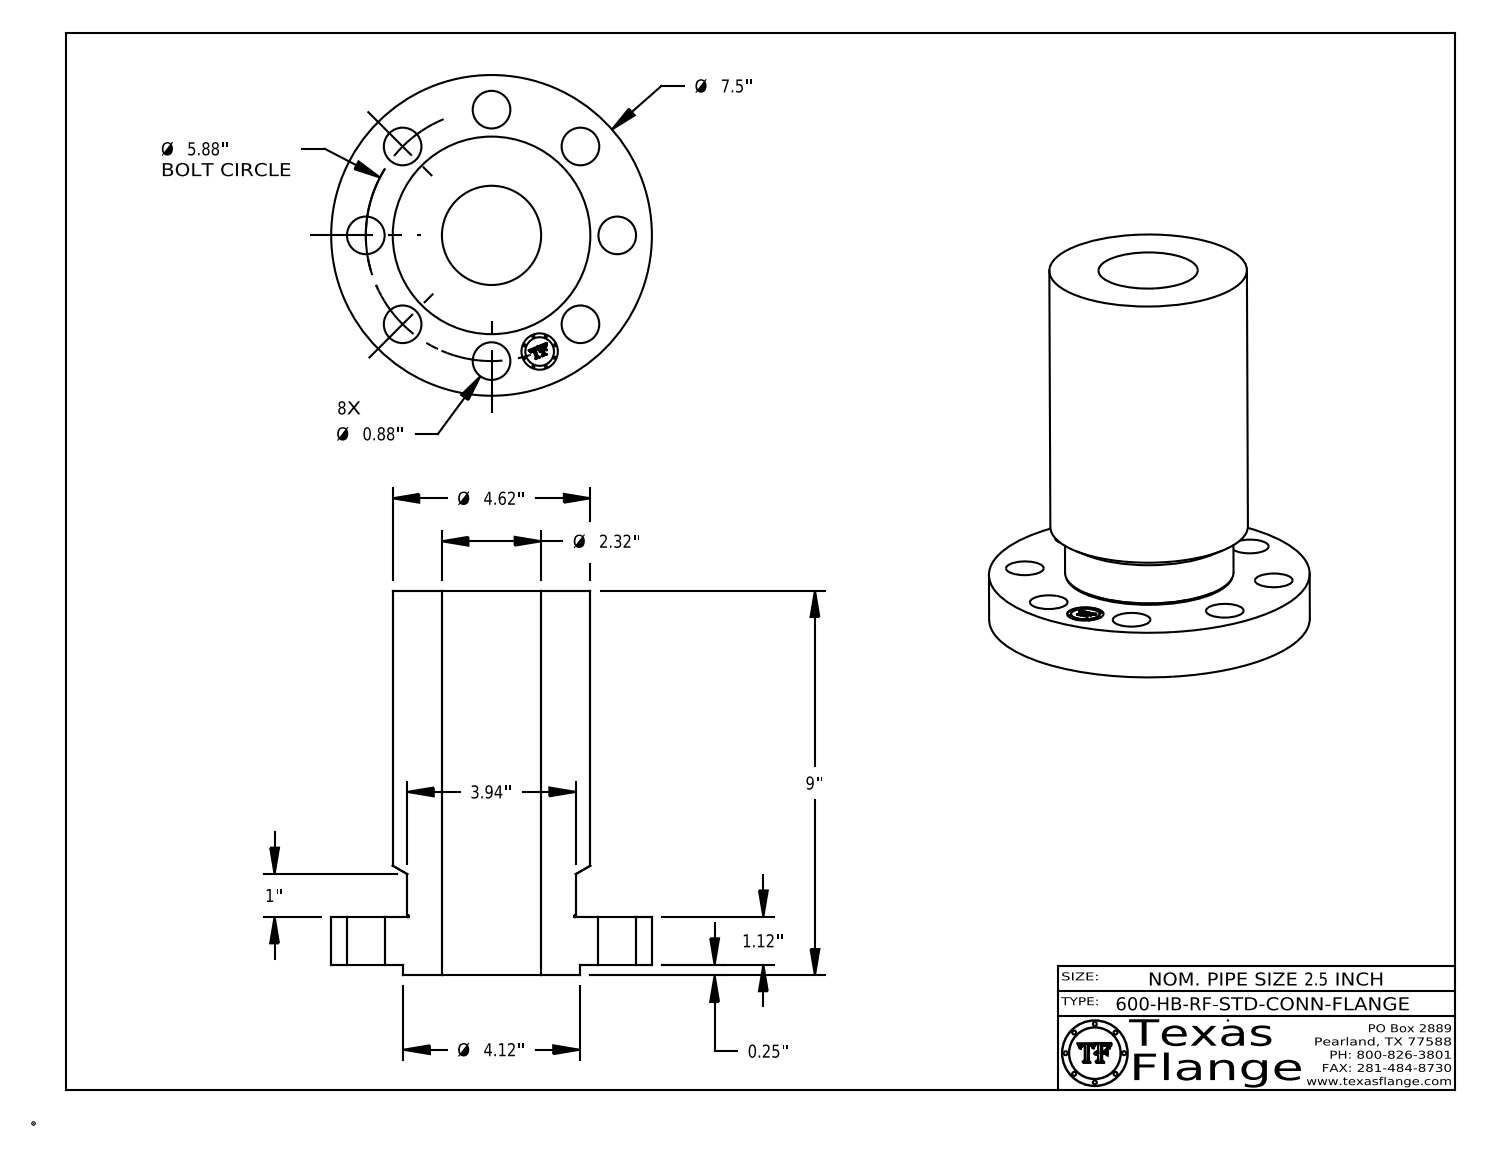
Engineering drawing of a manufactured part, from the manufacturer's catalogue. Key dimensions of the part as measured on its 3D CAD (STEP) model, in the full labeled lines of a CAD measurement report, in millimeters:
Part name (STEP PRODUCT): 2.5-600-HB-RF-STD-CONN-FLANGE
STEP written by: CATIA V5 STEP AP214 (AUTOMOTIVE_DESIGN)
Units: millimetres
Bodies: 1 solid, 421 faces (369 planar, 46 cylindrical, 6 other)
Overall size (bounding box): 228.6 × 190.5 × 190.5
Volume: 2 166 000 mm³ · Surface area: 197 600 mm²
Round holes (diameter × count): ⌀22.4 ×8, ⌀21.6 ×1, ⌀58.9 ×1
Round bosses / shafts (diameter × count): ⌀1.3 ×8, ⌀190.5 ×1, ⌀117.3 ×1, ⌀104.6 ×1, ⌀100.1 ×1, ⌀17 ×1
Main face-to-face distances: 28.4, 222.3, 193.8, 6.4, 34.8, 228.6, 34.7, 28.3, 193.9, 6.5
Hole centre spacings: 57.2, 138, 74.7, 74.7, 105.6, 105.6, 83, 149.4
